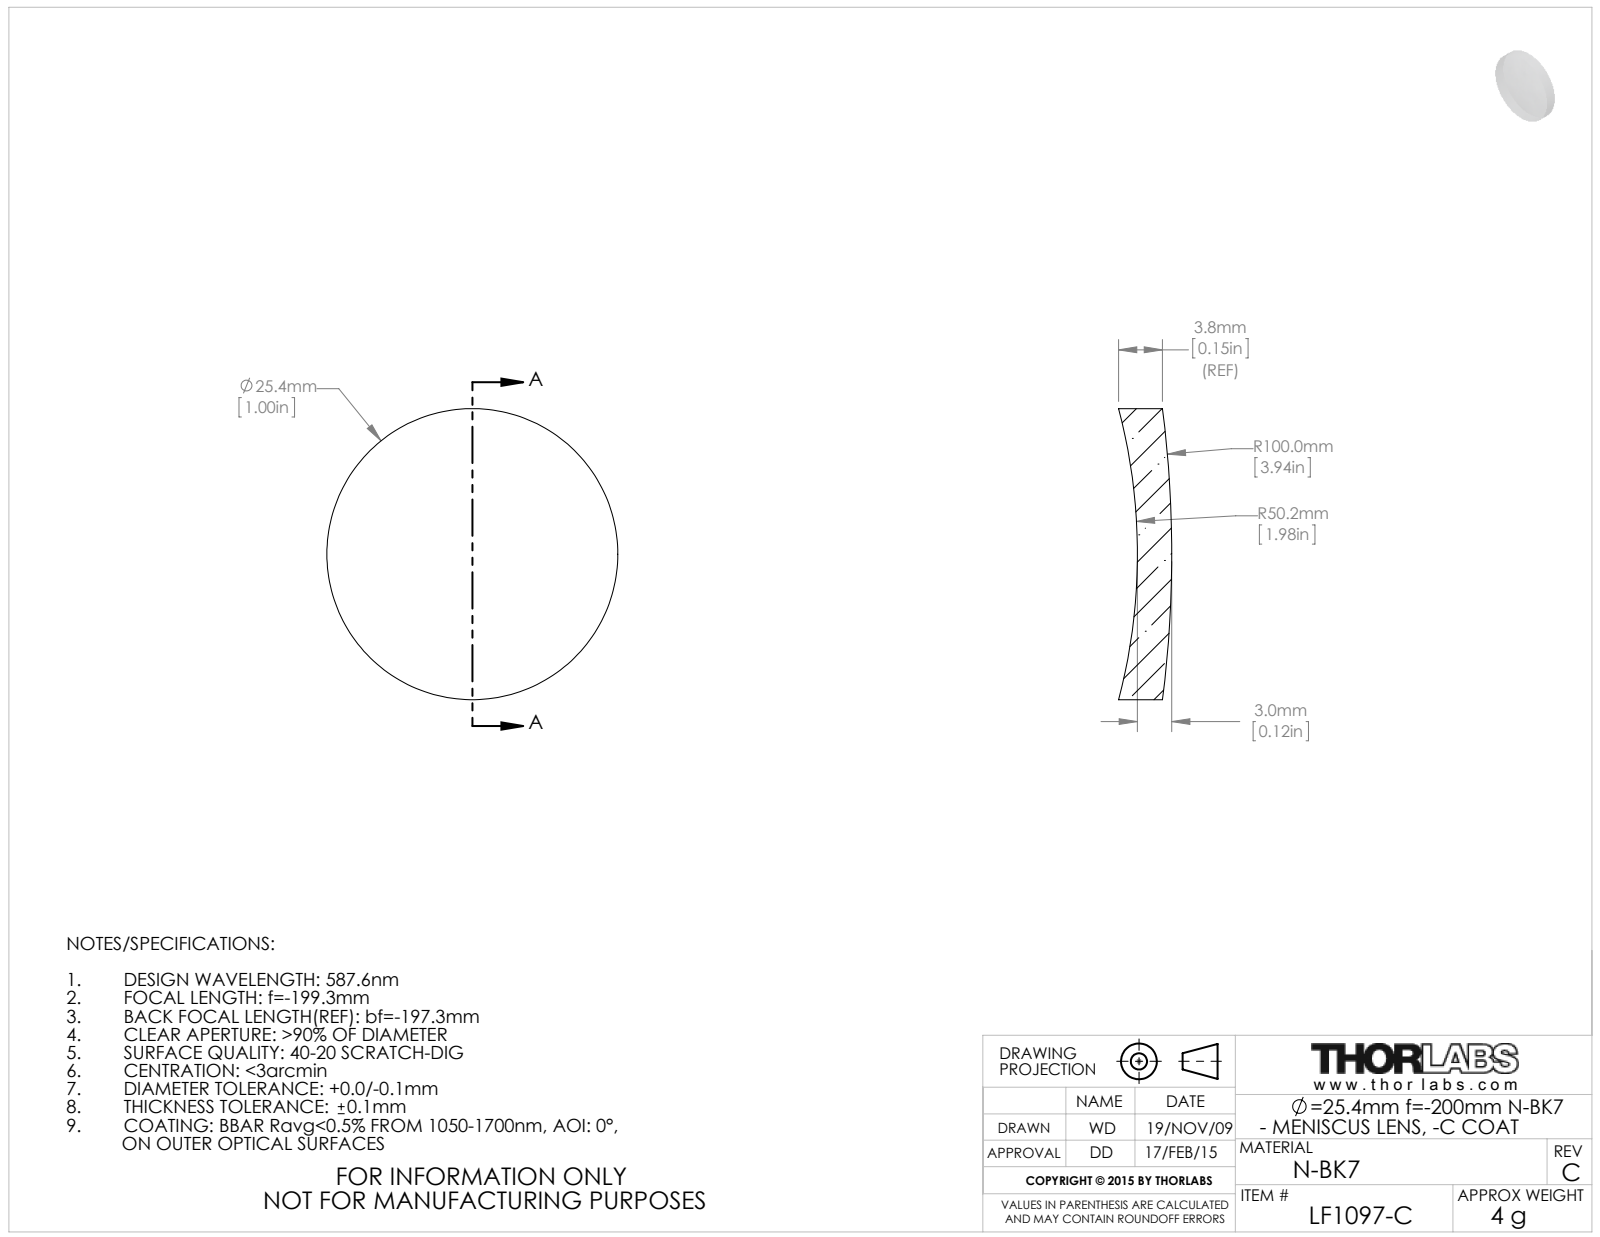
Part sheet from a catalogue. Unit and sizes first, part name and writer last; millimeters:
Units: millimetres
Overall size (bounding box): 25.4 × 25.4 × 4.63
Round bosses / shafts (diameter × count): ⌀25.4 ×1
Volume: 1 727 mm³ · Surface area: 1 329 mm²
Bodies: 1 solid, 6 faces (0 planar, 2 cylindrical, 4 other)
Part name (STEP PRODUCT): 4908-E0W
STEP written by: SolidWorks 2009 (AUTOMOTIVE_DESIGN)
